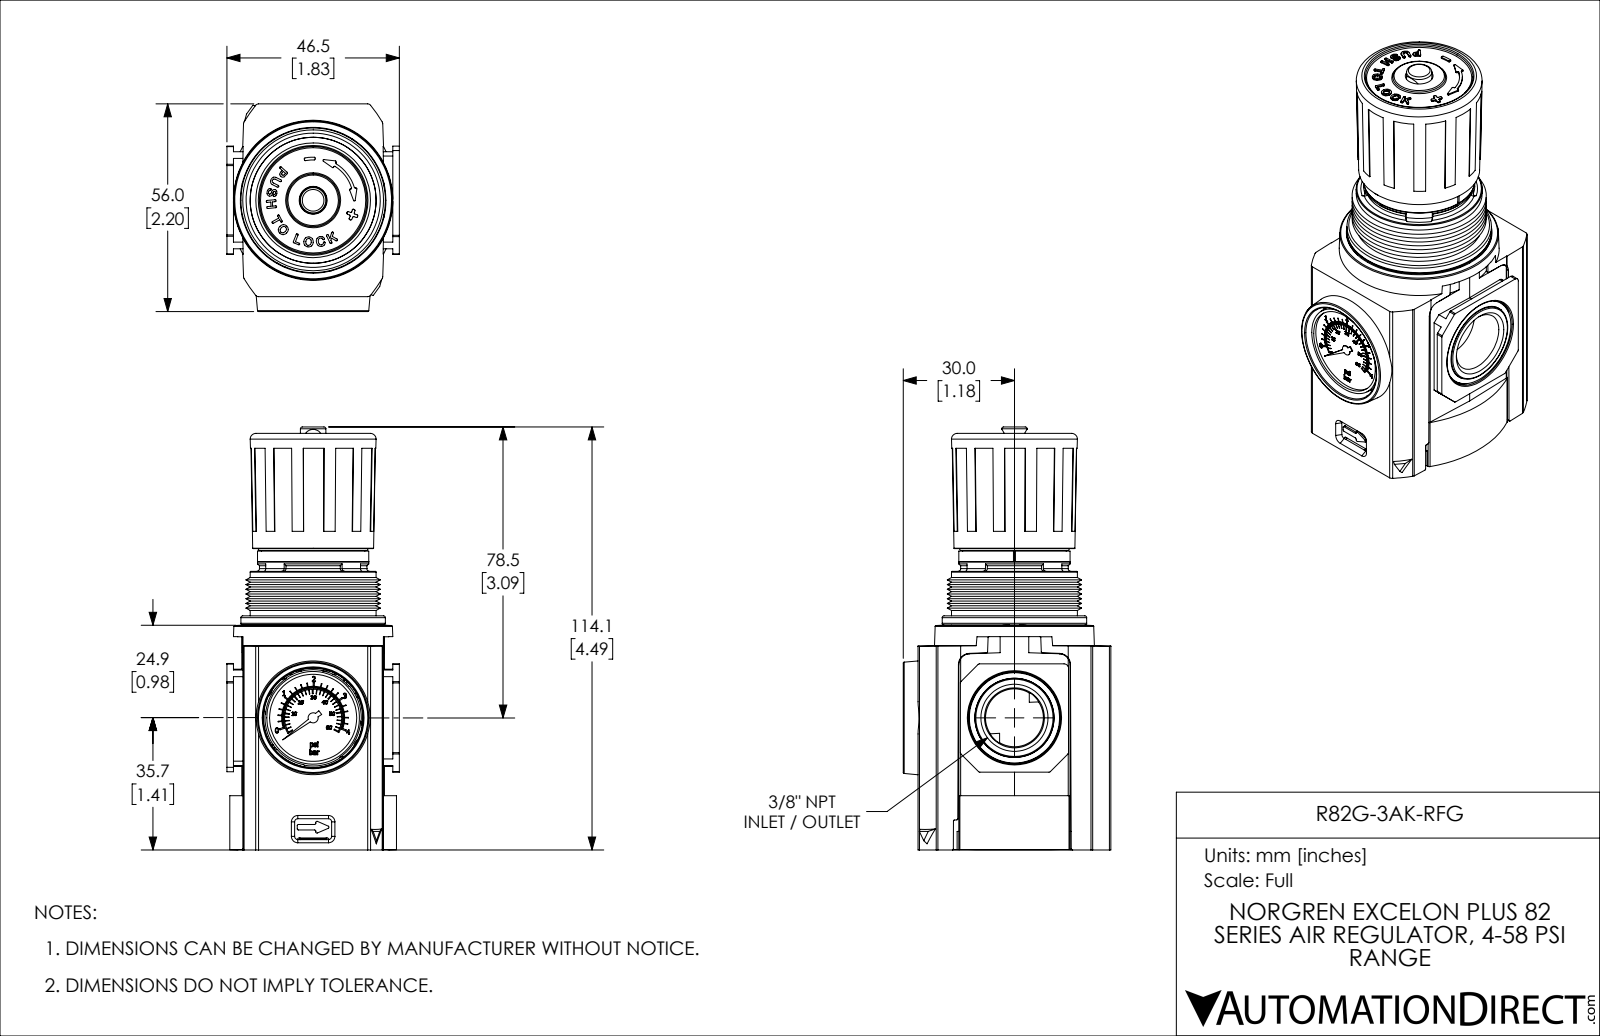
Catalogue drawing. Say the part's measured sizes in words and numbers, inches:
The part is named "R82G-3AK-RFG". Its 3-D file was written by "SolidWorks 2021 (CONFIG_CONTROL_DESIGN)". It is 5 solids with 2012 faces: 726 planar, 959 cylindrical and 327 other. Overall it measures 4.492 by 2.205 by 1.831 inches. Its volume is 8.84 cubic inches and its surface area 87.07 square inches. Round holes: 4 of diameter 0.097, 2 of diameter 0.138, 1 of diameter 0.128, 1 of diameter 0.197, 1 of diameter 0.236, 1 of diameter 0.886, 1 of diameter 0.925, 1 of diameter 1.102, 1 of diameter 1.354. Round bosses or shafts: 2 of diameter 0.224, 2 of diameter 0.118, 1 of diameter 1.535, 1 of diameter 1.339, 1 of diameter 1.181, 1 of diameter 1.161, 1 of diameter 1.138, 1 of diameter 1.098. Partial cylindrical surfaces (rounded edges, fillets, slot ends): 68 of radius 0.039, 39 of radius 0.02, 25 of radius 0.009, 12 of radius 0.006, 12 of radius 0.012, 12 of radius 0.031, 10 of radius 0.118, 9 of radius 0.01. The main face-to-face distances are 0.059, 1.988, 0.182, 1.352, 0.354, 1.417, 1.475, 0.123, 1.293, 1.169. The hole center spacings are 0.63, 1.091, 1.26, 2.705, 3.325, 2.965.
